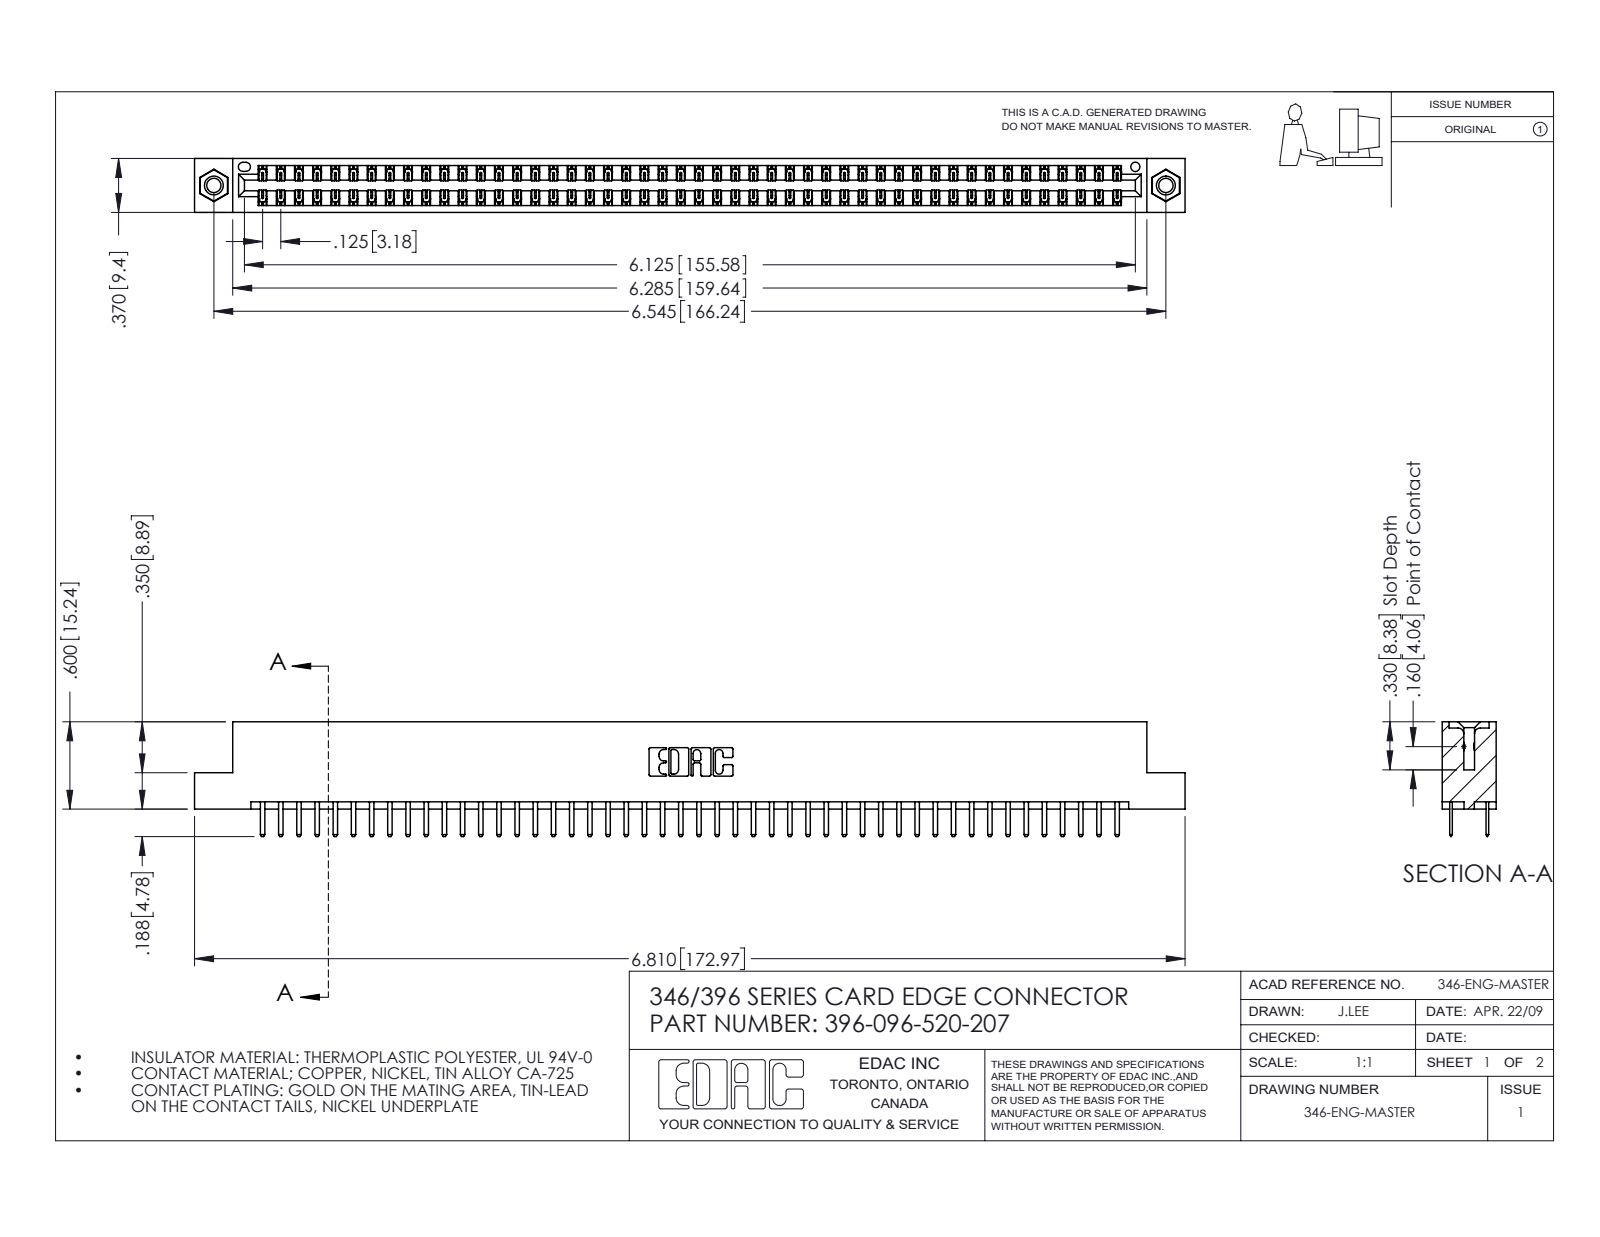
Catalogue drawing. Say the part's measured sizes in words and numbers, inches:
The part is named "345-292-001_345-293-120; 346 Part_Flush Mounting Lugs - 0.156 Dia-TI; 396-096-520-207; 345-250-001_345-250-005-103". Its 3-D file was written by "SolidWorks 2016 (CONFIG_CONTROL_DESIGN)". It is 99 solids with 5558 faces: 3660 planar, 1882 cylindrical and 16 other. Overall it measures 6.81 by 0.788 by 0.37 inches. Its volume is 1.029 cubic inches and its surface area 35.96 square inches. Round holes: 2 of diameter 0.098, 2 of diameter 0.125, 2 of diameter 0.156, 1 of diameter 0.064. Round bosses or shafts: 2 of diameter 0.155. Partial cylindrical surfaces (rounded edges, fillets, slot ends): 144 of radius 0.006, 100 of radius 0.01, 22 of radius 0.01, 6 of radius 0.007, 6 of radius 0.031, 3 of radius 0.026, 2 of radius 0.014, 2 of radius 0.022. The main face-to-face distances are 0.048, 0.322, 0.25, 0.37, 0.275, 0.072, 0.298, 0.025, 0.148, 0.222. The hole center spacings are 0.246, 6.336, 6.545.
